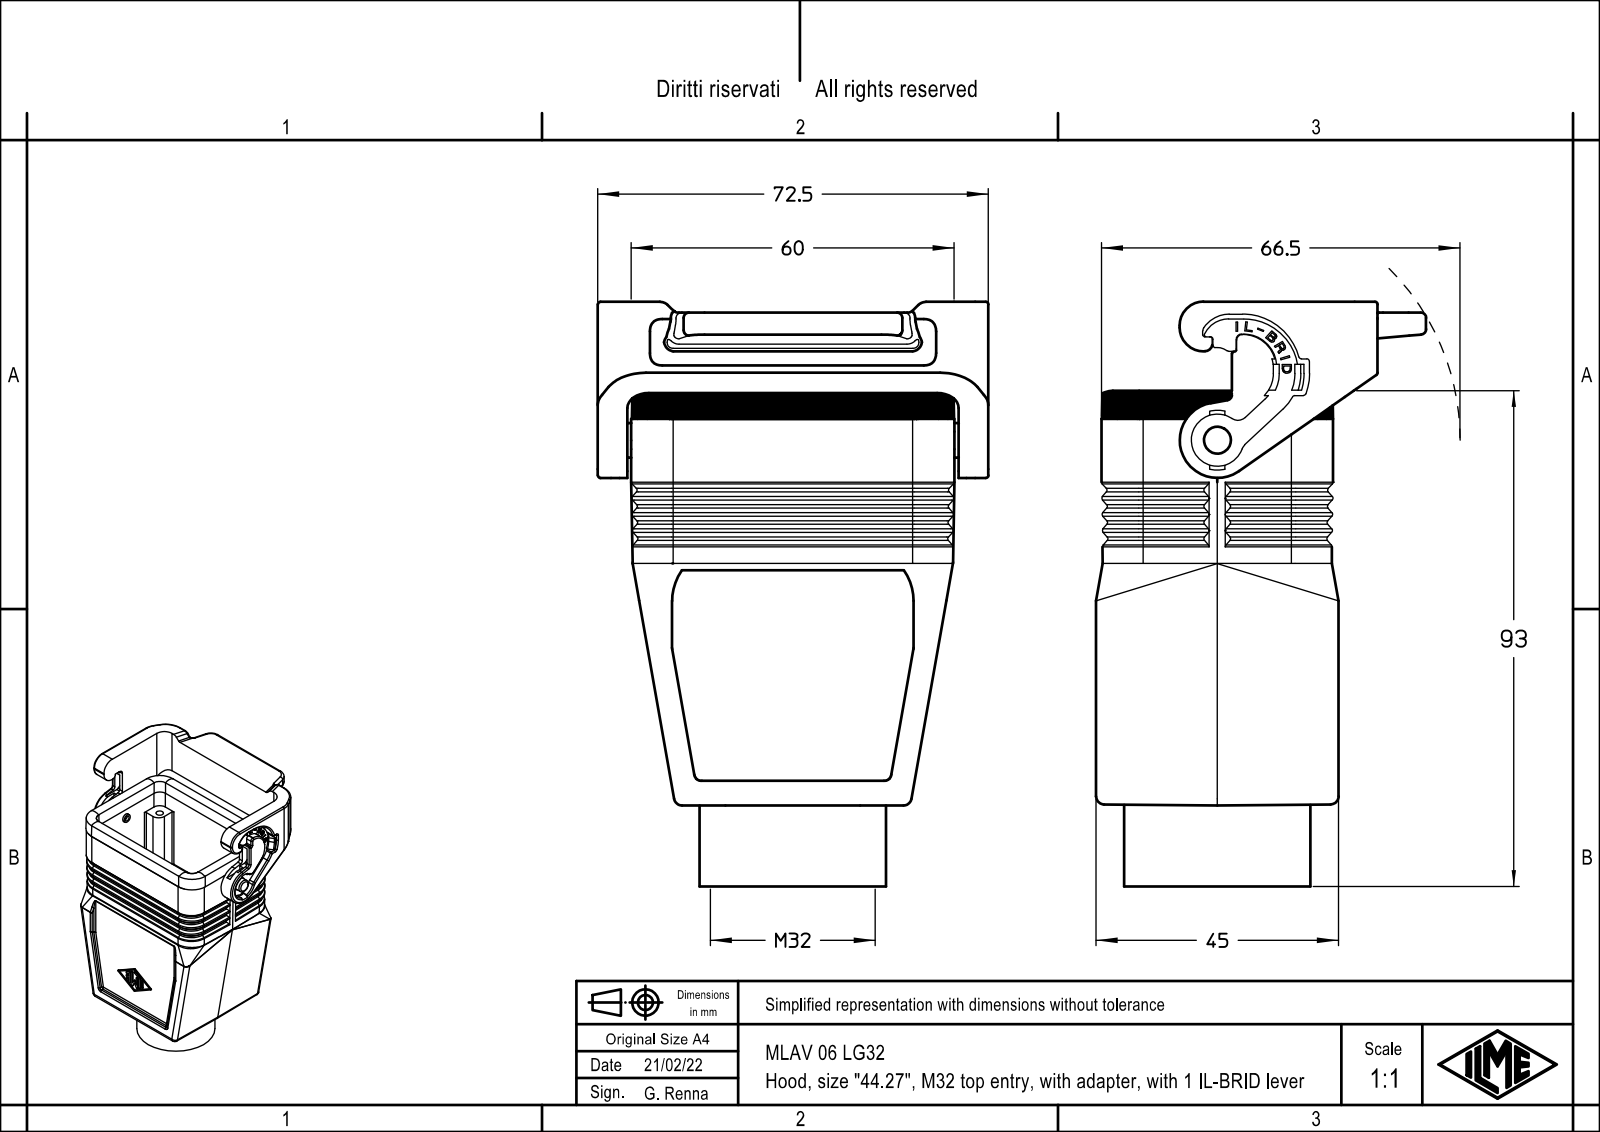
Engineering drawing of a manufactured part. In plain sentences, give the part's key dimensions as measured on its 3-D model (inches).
The part is named "MLAV_06_LG32". Its 3-D file was written by "Creo Elements/Direct Modeling 20.1B 02-Apr-2019 (C) Parametric Technology GmbH (AUTOMOTIVE_DESIGN)". It is 1 solid with 989 faces: 589 planar, 261 cylindrical and 139 other. Overall it measures 4.309 by 2.854 by 2.411 inches. Its volume is 5.025 cubic inches and its surface area 65.43 square inches. Round holes: 4 of diameter 0.108, 1 of diameter 1.063, 1 of diameter 1.26. Round bosses or shafts: 1 of diameter 1.417, 1 of diameter 0.268, 1 of diameter 0.189. Partial cylindrical surfaces (rounded edges, fillets, slot ends): 57 of radius 0.02, 43 of radius 0.039, 16 of radius 0.059, 16 of radius 0.118, 15 of radius 0.013, 14 of radius 0.276, 4 of radius 0.012, 4 of radius 0.079. The main face-to-face distances are 1.545, 0.148, 1.693, 0.039, 0.187, 0.276, 0.144, 1.358, 1.506, 1.398. The hole center spacings are 1.016, 1.063, 1.732, 2.032.
